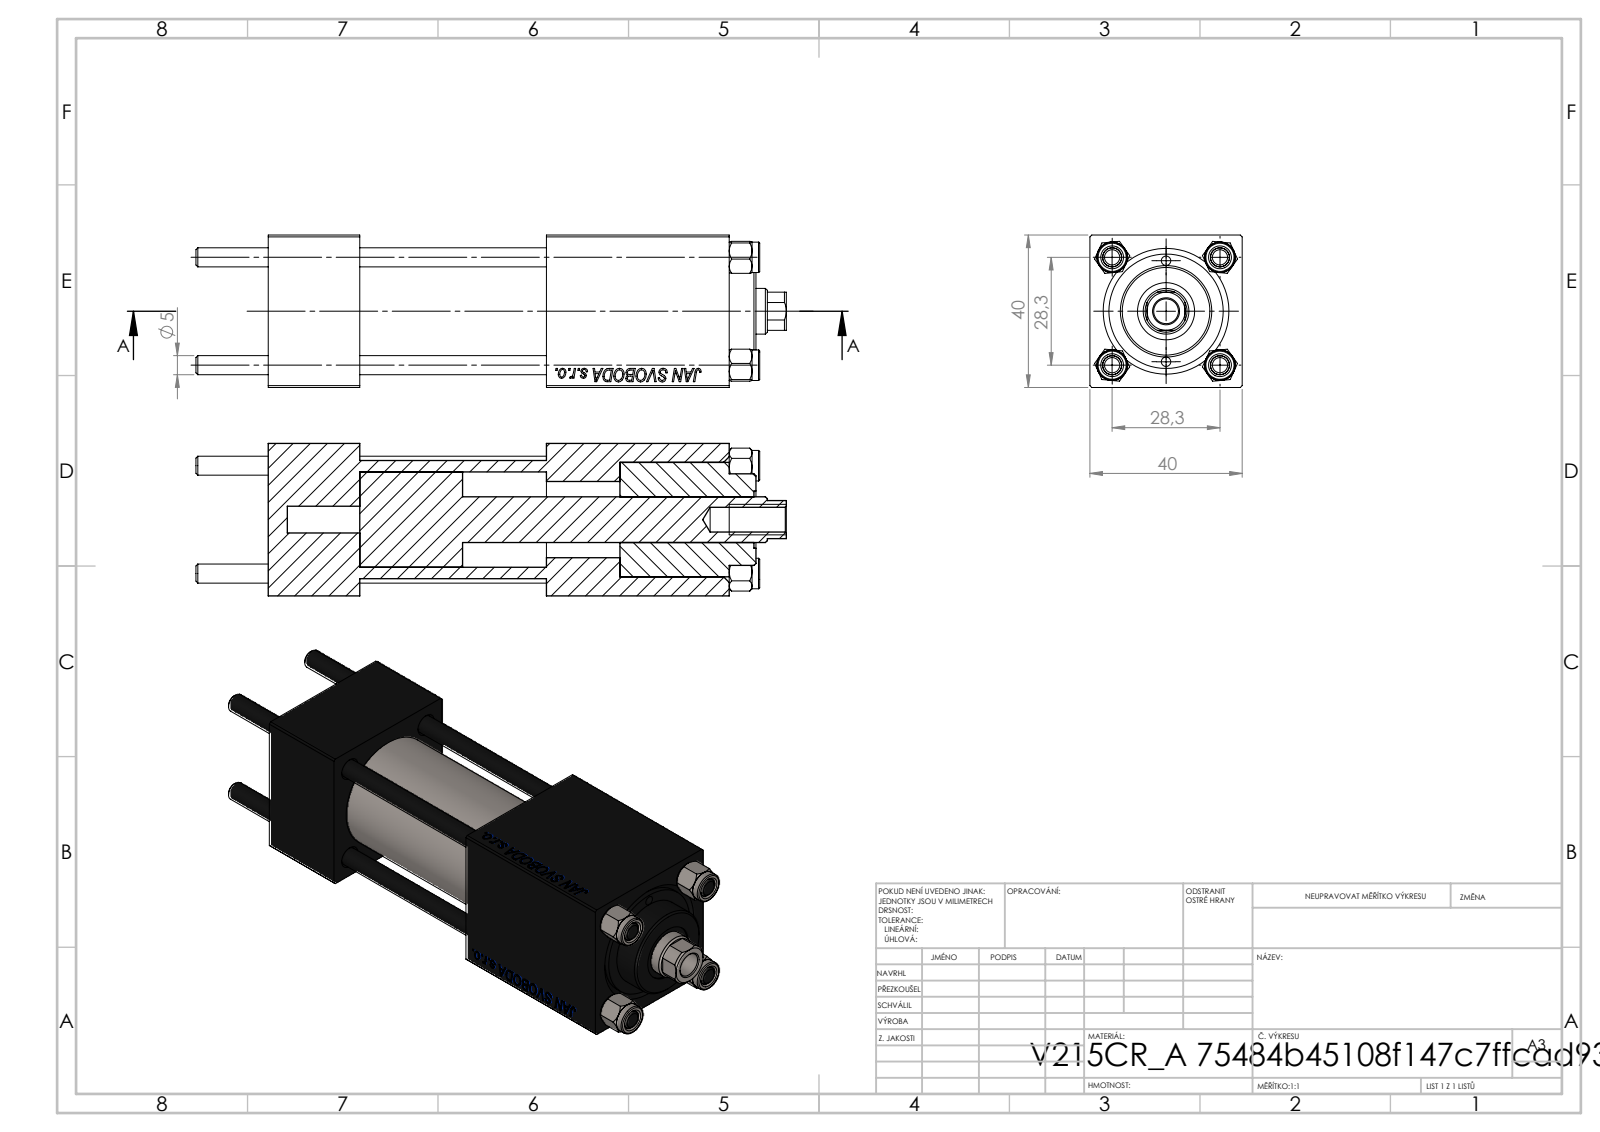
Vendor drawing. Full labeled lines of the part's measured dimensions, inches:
Part name (STEP PRODUCT): CR025_012_A_0_G_A_G_M_020_+#_##_TYCINKA; NUT_M5; V215CR_BODY_A; V215CR_VCP (+1 more)
STEP written by: SolidWorks 2019 (CONFIG_CONTROL_DESIGN)
Units: inches
Bodies: 11 solids, 1137 faces (519 planar, 82 cylindrical, 536 other)
Overall size (bounding box): 6.102 × 1.575 × 1.575
Volume: 8.89 in³ · Surface area: 92.23 in²
Round holes (diameter × count): ⌀0.197 ×4, ⌀0.787 ×3, ⌀0.098 ×2, ⌀0.276 ×2, ⌀0.518 ×2, ⌀0.256 ×1, ⌀0.472 ×1, ⌀0.591 ×1, ⌀0.984 ×1, ⌀1.181 ×1
Round bosses / shafts (diameter × count): ⌀0.315 ×4, ⌀1.22 ×1, ⌀0.945 ×1
Partial cylindrical surfaces — rounded edges, fillets, slot ends (radius × count): R0.217 ×1
Main face-to-face distances: 1.575, 0.945, 3.634, 2.689, 4.764, 3.819, 1.13, 2.874, 1.929, 0.76
Hole centre spacings: 0.558, 0.788, 1.114, 1.214, 0.522, 1.576, 1.043, 2.913
